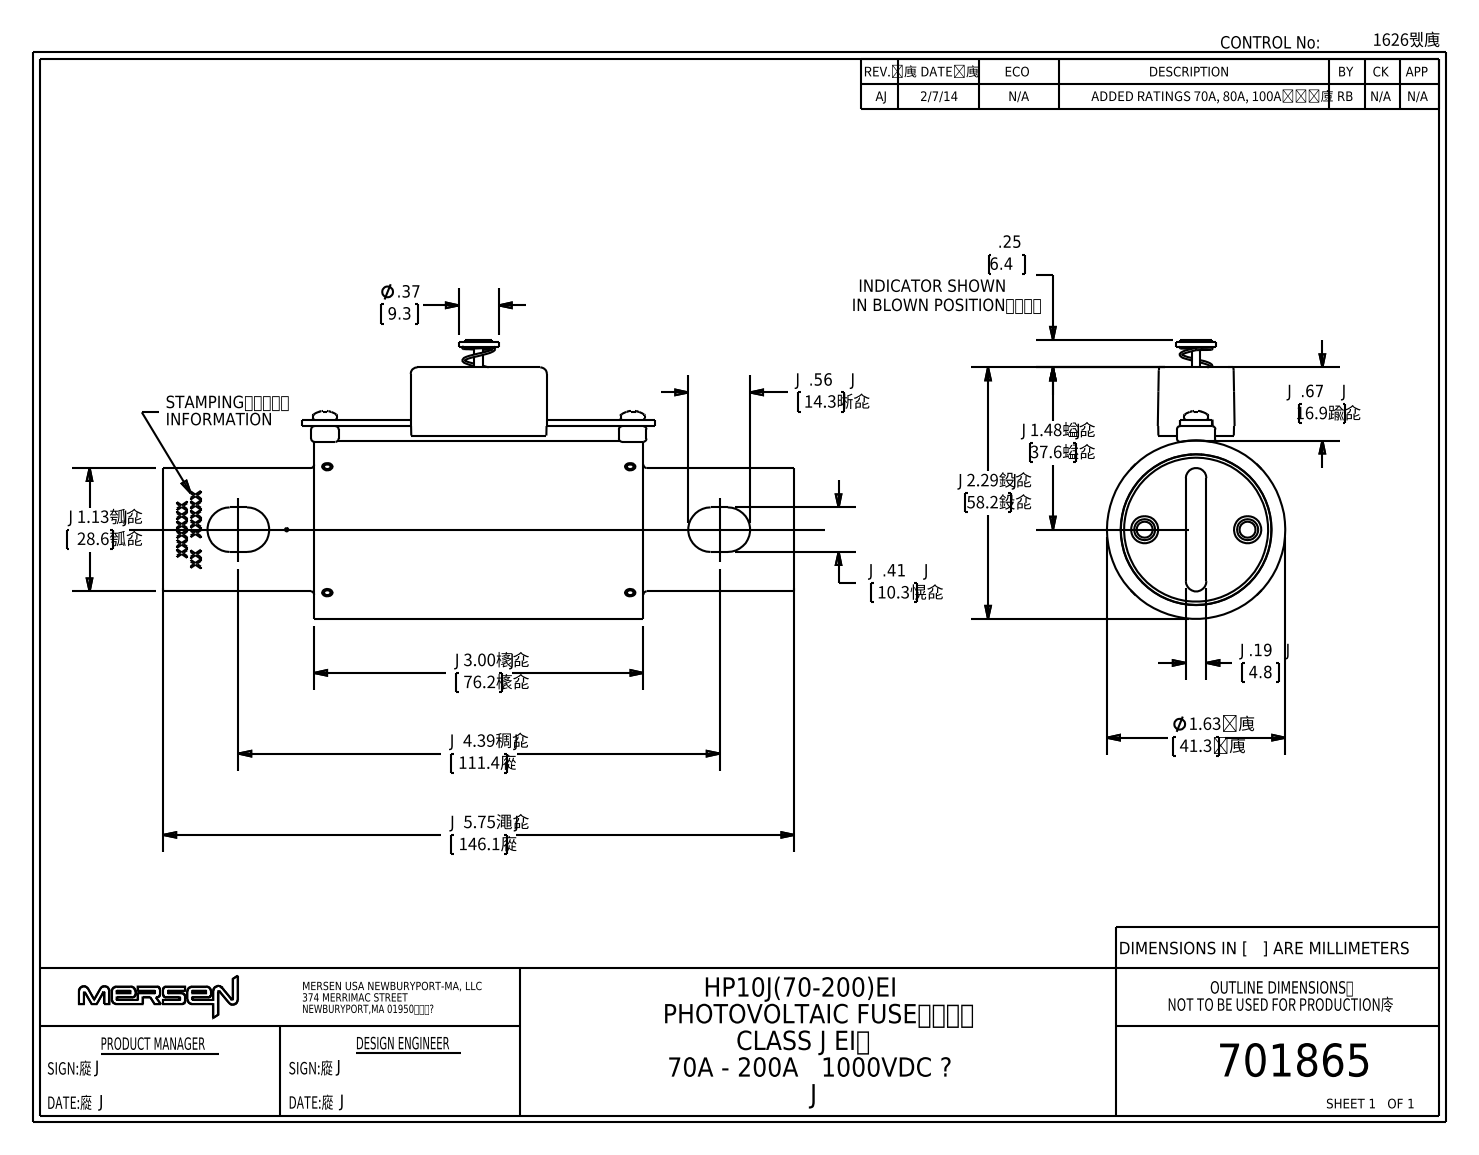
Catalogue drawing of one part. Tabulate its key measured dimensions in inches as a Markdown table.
| quantity | value |
| --- | --- |
| part name | 701865reva |
| STEP written by | SolidWorks 2014 (AUTOMOTIVE_DESIGN) |
| units | inches |
| bodies | 26 solids, 2028 faces (691 planar, 804 cylindrical, 533 other) |
| overall size | 5.75 × 2.292 × 1.625 |
| volume | 3.372 in³ |
| surface area | 59.02 in² |
| round holes (diameter × count) | 0.094 × 4, 0.17 × 3, 0.101 × 2, 0.125 × 2, 0.146 × 2, 0.188 × 2, 1.375 × 1 |
| round bosses / shafts (diameter × count) | 0.219 × 2, 0.192 × 2, 0.112 × 2, 0.08 × 2, 1.625 × 1, 1.372 × 1, 0.365 × 1, 0.081 × 1 |
| partial cylindrical surfaces (radius × count) | 4 × 44, 0.03 × 26, 0.005 × 14, 0.02 × 10, 0.06 × 10, 0.07 × 4, 0.203 × 4, 0.08 × 2 |
| main face-to-face distances | 0.25, 2.75, 0.187, 3, 2.5, 0.06, 0.08, 0.139, 0.084, 0.535 |
| hole center spacings | 0.19, 0.469, 1.212, 1.402, 1.592, 2.76, 0.38, 0.938 |
